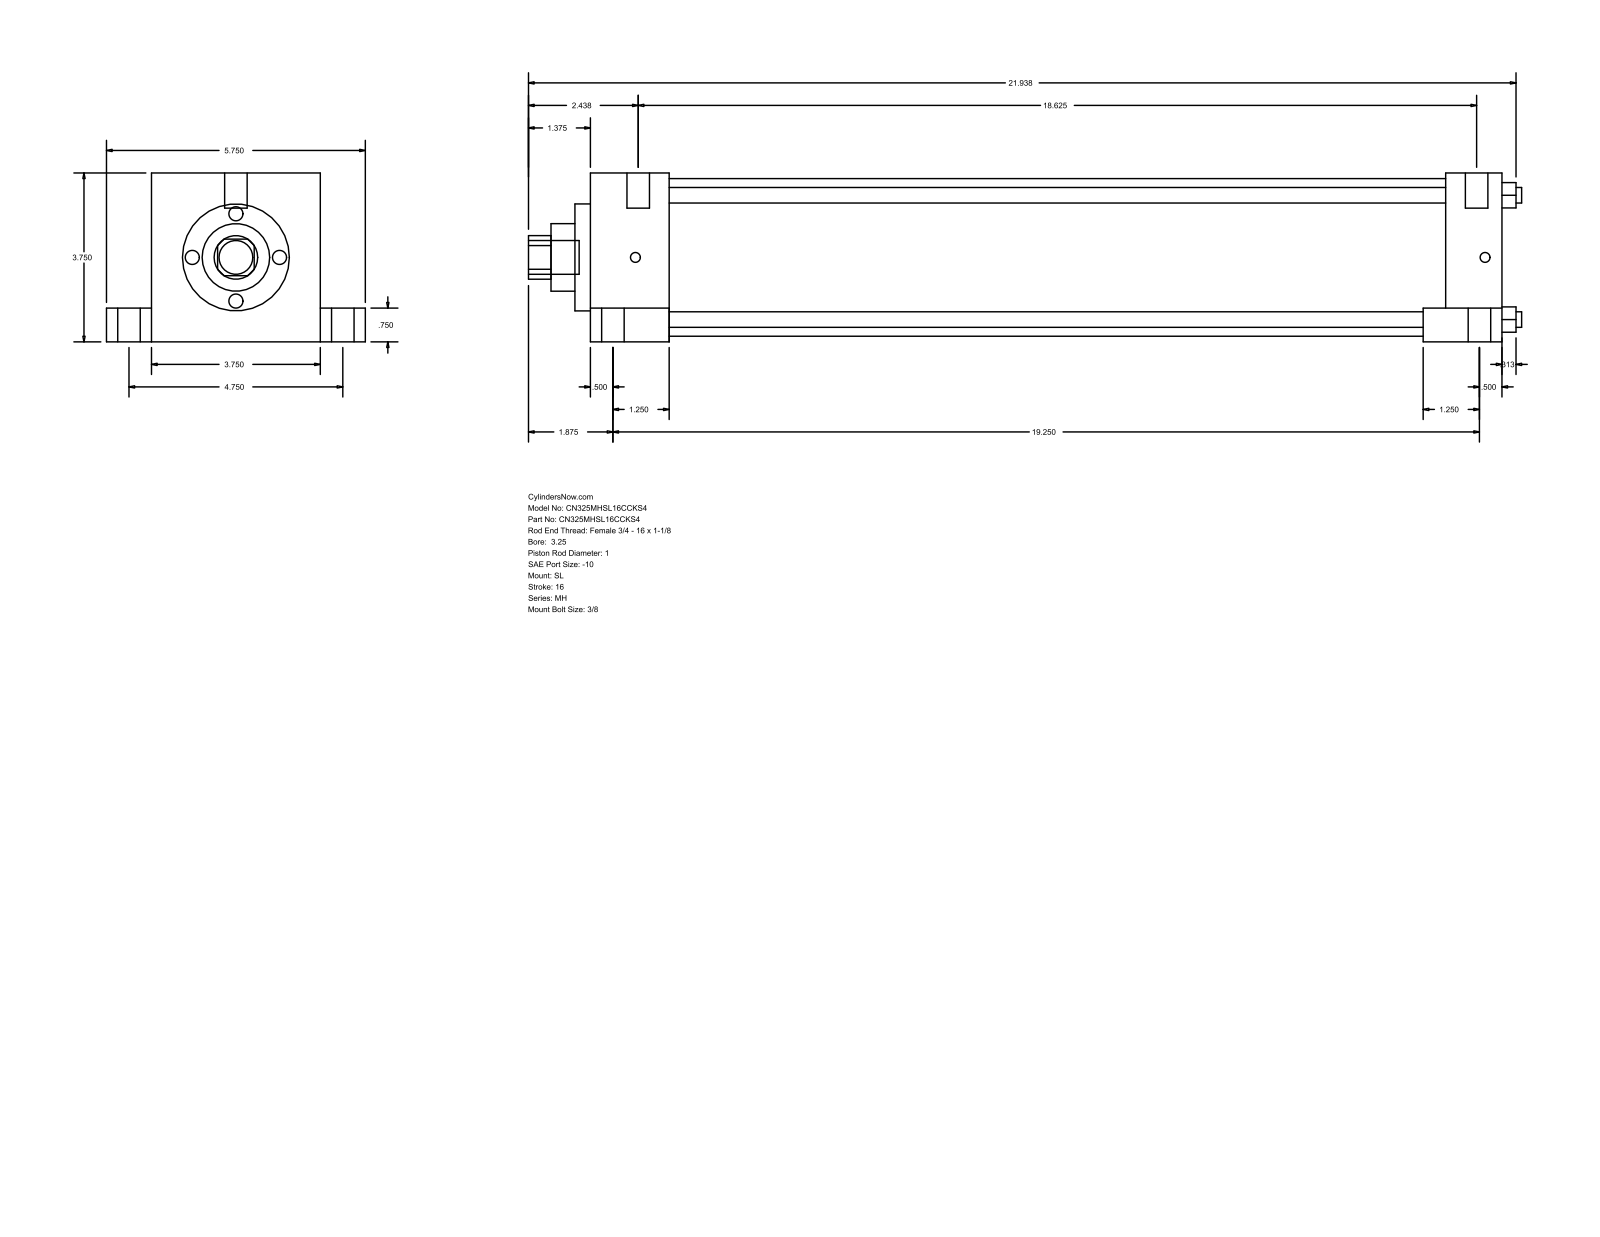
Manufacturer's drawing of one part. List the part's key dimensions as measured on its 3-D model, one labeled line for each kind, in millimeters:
Part name (STEP PRODUCT): MH_SL__0325_1
STEP written by: GSSL Pune (CONFIG_CONTROL_DESIGN)
Units: millimetres
Bodies: 0 solids, 110 faces (77 planar, 33 cylindrical, 0 other)
Overall size (bounding box): 560.39 × 146.05 × 95.25
Round holes (diameter × count): ⌀8.76 ×4, ⌀25.4 ×1, ⌀38.1 ×1, ⌀60.33 ×1, ⌀88.9 ×1
Round bosses / shafts (diameter × count): ⌀12.7 ×6, ⌀19.05 ×5, ⌀5.56 ×4
Partial cylindrical surfaces — rounded edges, fillets, slot ends (radius × count): R12.29 ×1
Main face-to-face distances: 95.24, 514.35, 44.46, 469.89, 25.41, 120.65, 19.05, 76.19, 482.6, 438.14
Hole centre spacings: 49.57, 70.1, 99.14
